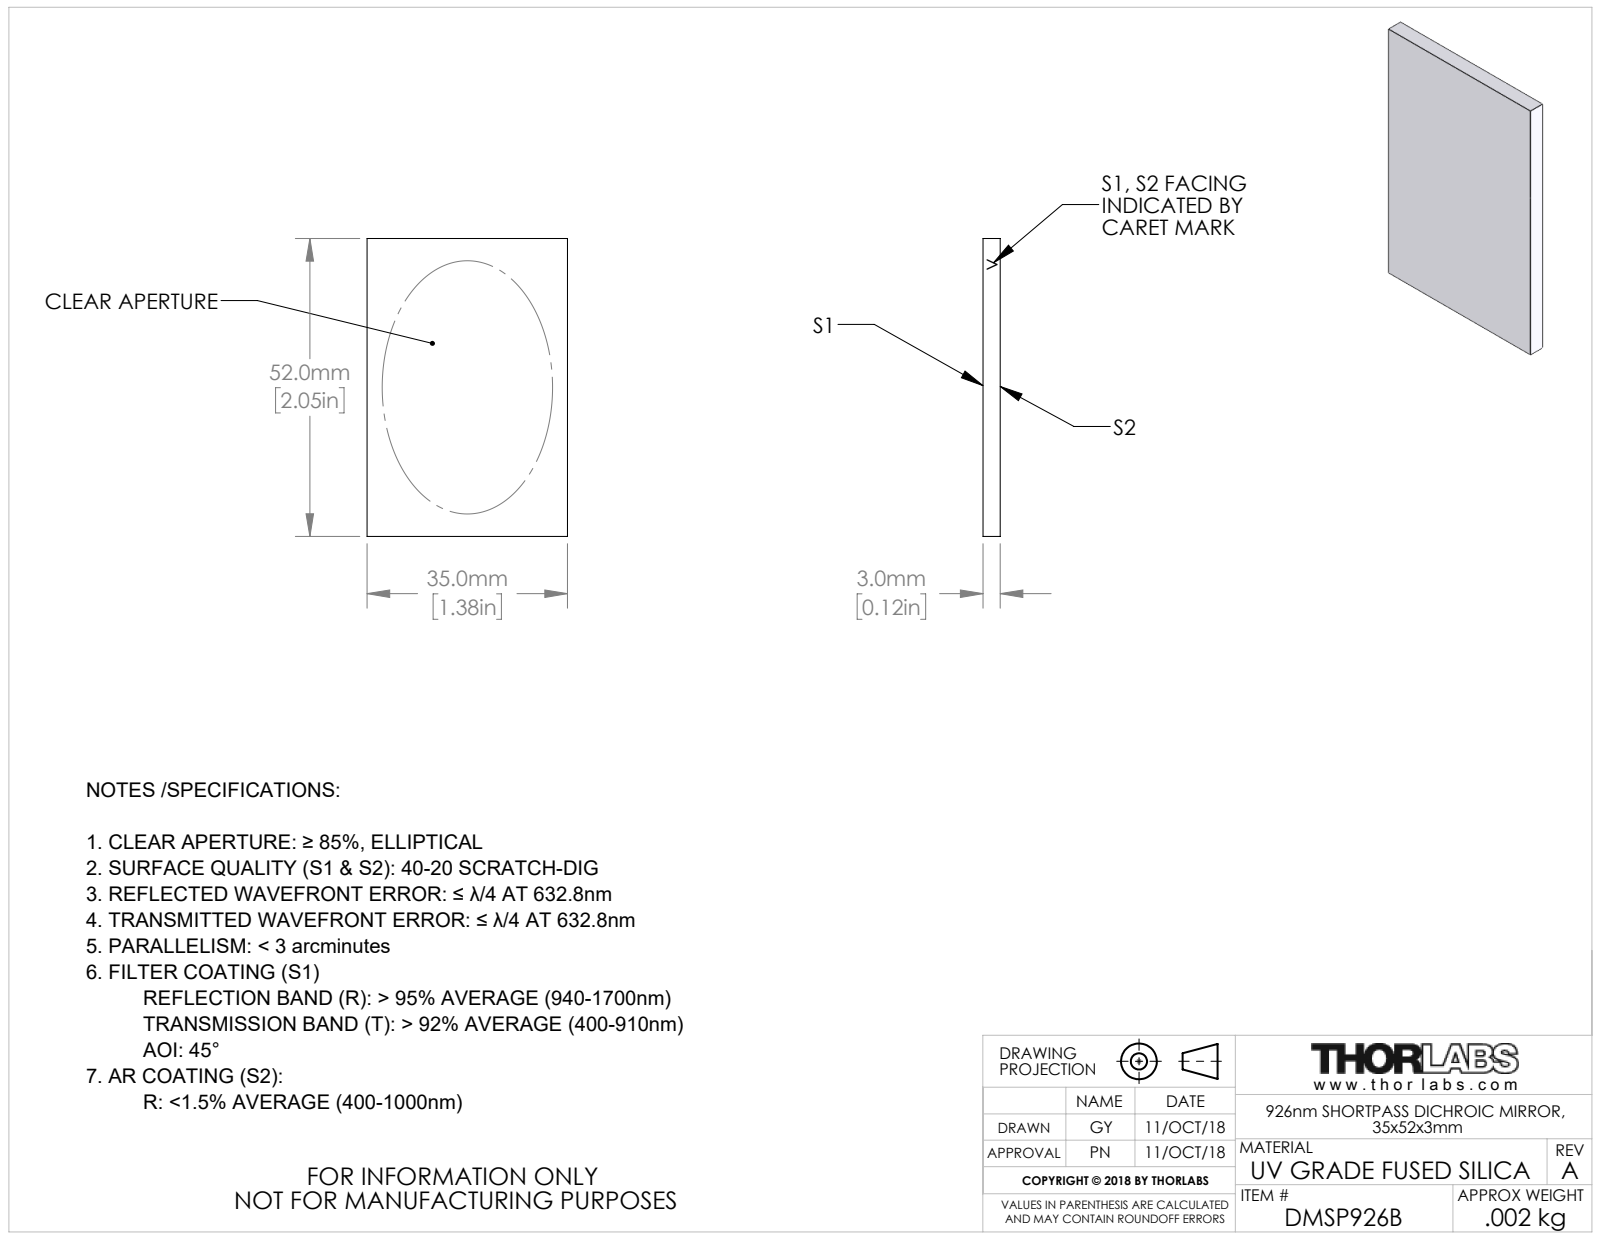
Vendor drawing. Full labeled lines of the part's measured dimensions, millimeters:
Part name (STEP PRODUCT): TTN166722-E0W
STEP written by: SolidWorks 2018 (AUTOMOTIVE_DESIGN)
Units: millimetres
Bodies: 1 solid, 6 faces (6 planar, 0 cylindrical, 0 other)
Overall size (bounding box): 52 × 35 × 3
Volume: 5 460 mm³ · Surface area: 4 162 mm²
Main face-to-face distances: 3, 35, 52
